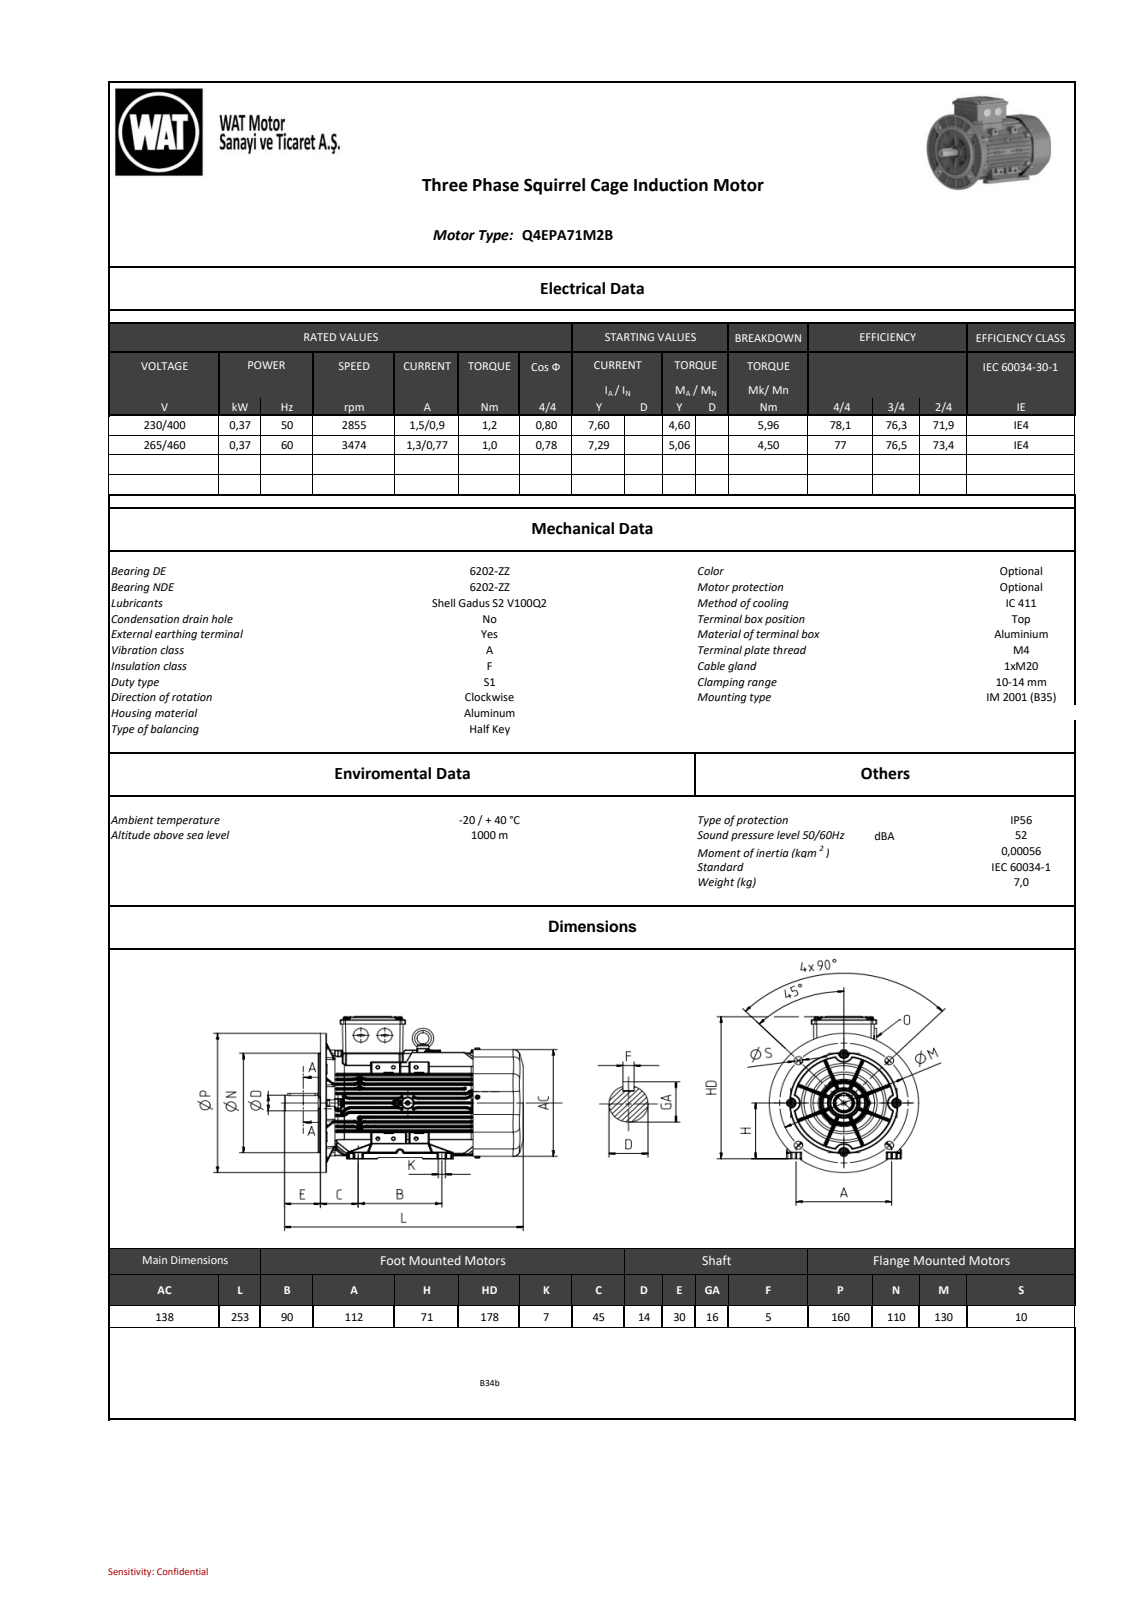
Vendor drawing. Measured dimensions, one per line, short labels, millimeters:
name: 001_objects
written by: SIEMENS PLM Software NX2206.8101 (AUTOMOTIVE_DESIGN)
unit: mm
bodies: 0 solids, 3210 faces (1439 planar, 847 cylindrical, 924 other)
size: 262 × 187.11 × 160
holes: 9× ⌀3.3, 8× ⌀3.65, 6× ⌀2.5, 5× ⌀5, 4× ⌀4, 4× ⌀4.5, 4× ⌀4.65, 4× ⌀4.8, 4× ⌀5.2, 4× ⌀7, 4× ⌀10, 3× ⌀3
bosses: 8× ⌀8, 8× ⌀4, 1× ⌀160, 1× ⌀138, 1× ⌀110, 1× ⌀61, 1× ⌀26, 1× ⌀25.28
rounds: 147× R1, 54× R0.5, 36× R1.2, 32× R2, 32× R10, 24× R1.5, 23× R4, 18× R0.75
face distances: 2, 3, 5, 1, 15, 197.5, 83, 189.2, 194.2, 4
hole spacings: 61.39, 87.43, 89.67, 89.74, 55, 36.59, 65, 67.18
